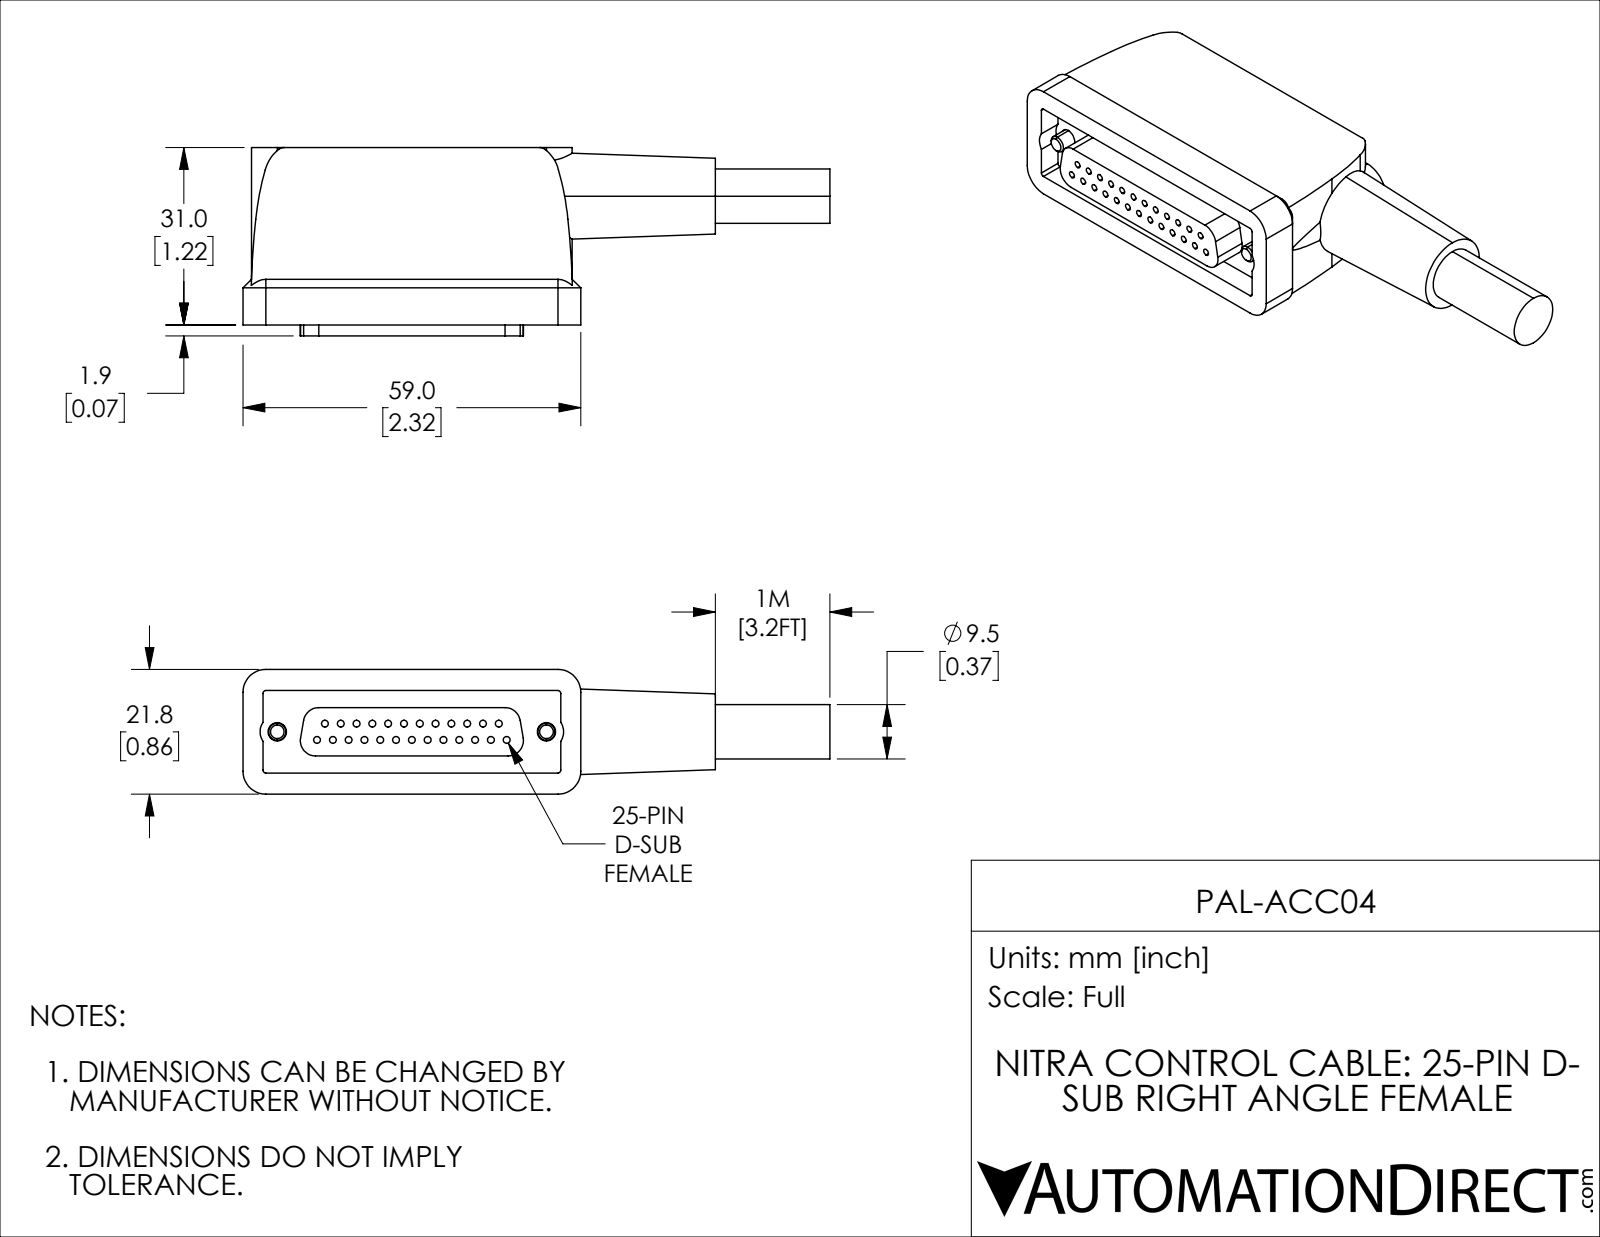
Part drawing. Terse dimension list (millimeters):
name: PAL-ACC04
written by: SolidWorks 2019 (CONFIG_CONTROL_DESIGN)
unit: mm
bodies: 1 solid, 186 faces (71 planar, 101 cylindrical, 14 other)
size: 102.5 × 32.9 × 21.8
volume: 37 542 mm³; area: 11 486 mm²
holes: 25× ⌀1.2, 2× ⌀3.2, 2× ⌀5
bosses: 2× ⌀4.6, 2× ⌀3, 1× ⌀9.5
rounds: 4× R0.5, 4× R2.68, 4× R4, 2× R1.4, 2× R3, 2× R4.5, 2× R6.5, 2× R50
face distances: 18.8, 1.5, 20.3, 31, 4.1, 26.9, 3.7, 18.1, 2.2, 16.6
hole spacings: 3.16, 2.76, 5.02, 5.52, 7.46, 8.28, 10.07, 11.04
